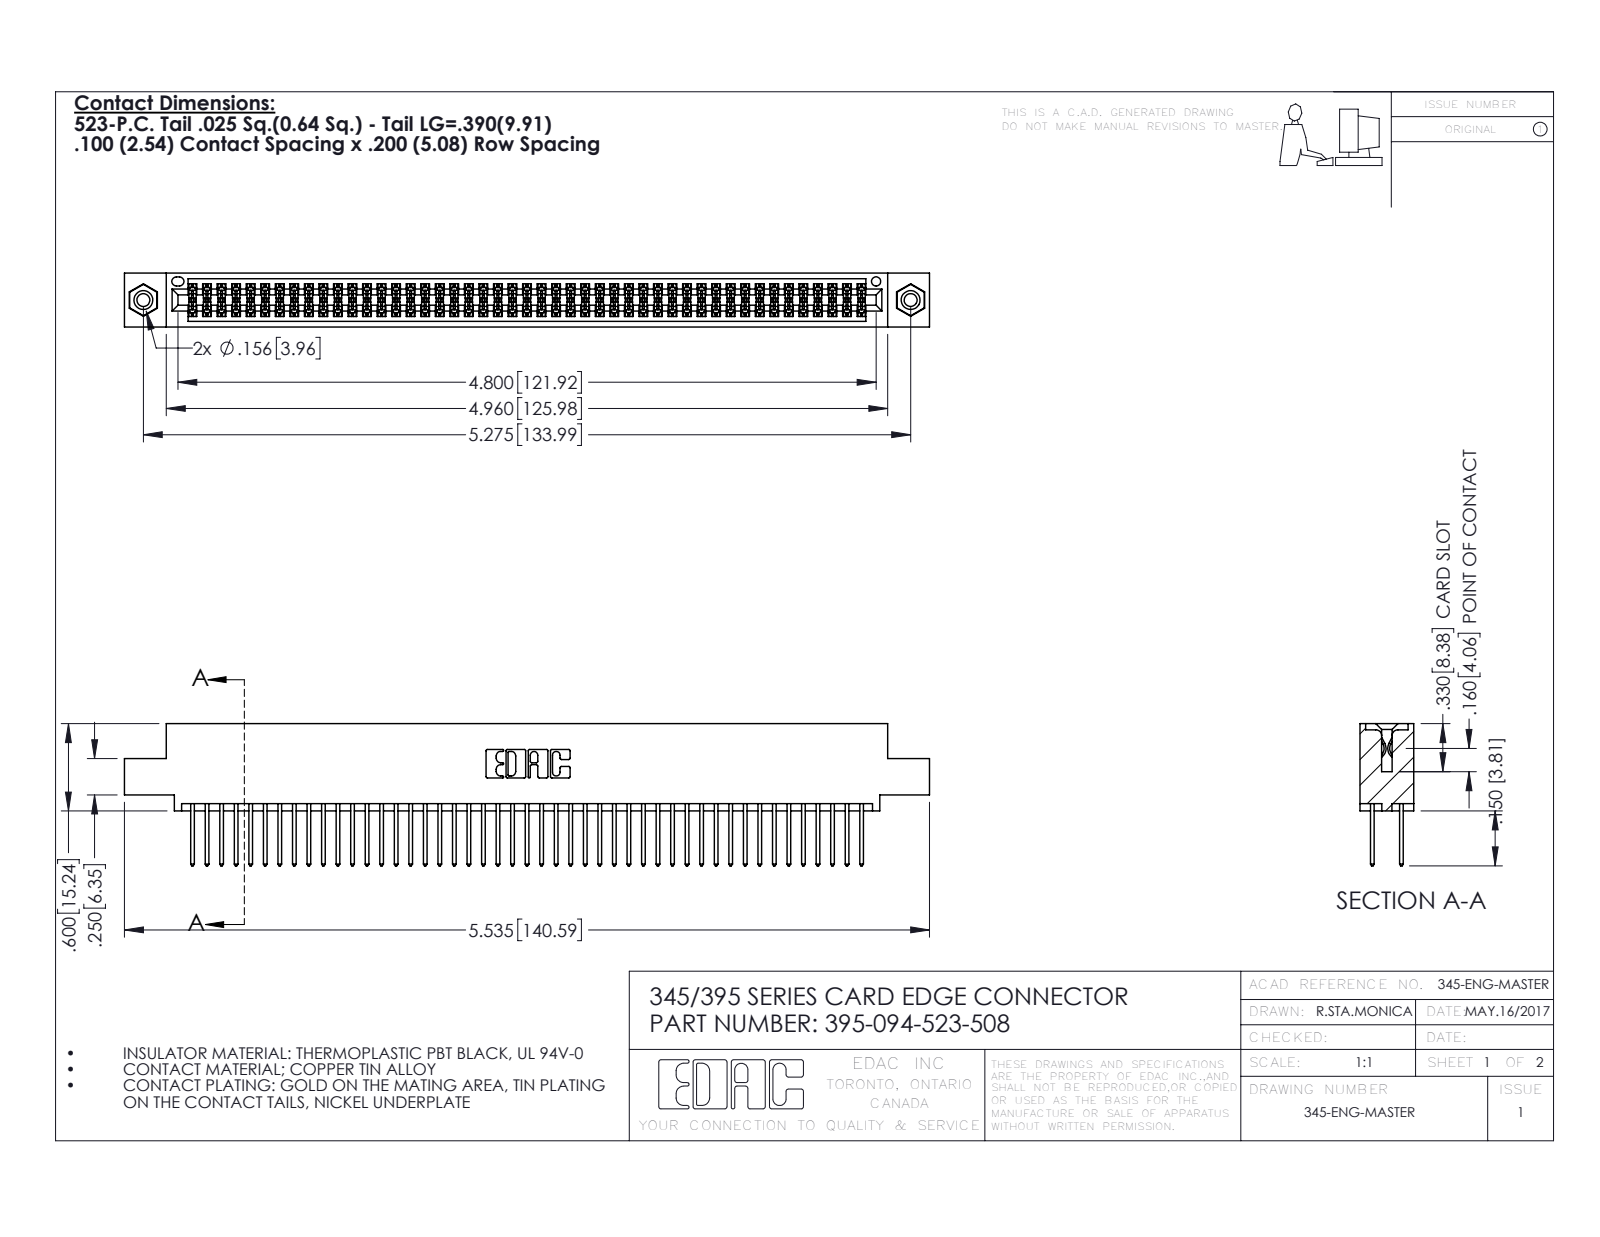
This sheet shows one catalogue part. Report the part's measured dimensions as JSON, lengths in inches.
{"part_name": "395-094-523-508; 345-250-001_345-250-003-102; 345 Part_0.110 Offset - 0.156 Dia-TI; 345-292-001_345-293-123", "step_written_by": "SolidWorks 2016 (CONFIG_CONTROL_DESIGN)", "units": "inches", "bodies": {"solids": 97, "faces": 4890, "planar": 3218, "cylindrical": 1656, "other": 16}, "overall_size": [5.535, 0.977, 0.37], "volume_in3": 0.843, "surface_area_in2": 33.31, "round_holes": [[0.089, 2], [0.125, 2], [0.156, 2], [0.064, 1]], "round_bosses_or_shafts": [[0.155, 2]], "partial_cylinders_radius": [[0.006, 141], [0.01, 94], [0.01, 22], [0.007, 6], [0.031, 6], [0.026, 3], [0.014, 2], [0.019, 2]], "face_to_face_distances": [0.072, 0.298, 0.2, 0.098, 0.272, 0.025, 0.37, 0.225, 0.175, 0.149], "hole_center_spacings": [0.27, 5.039, 5.275]}
